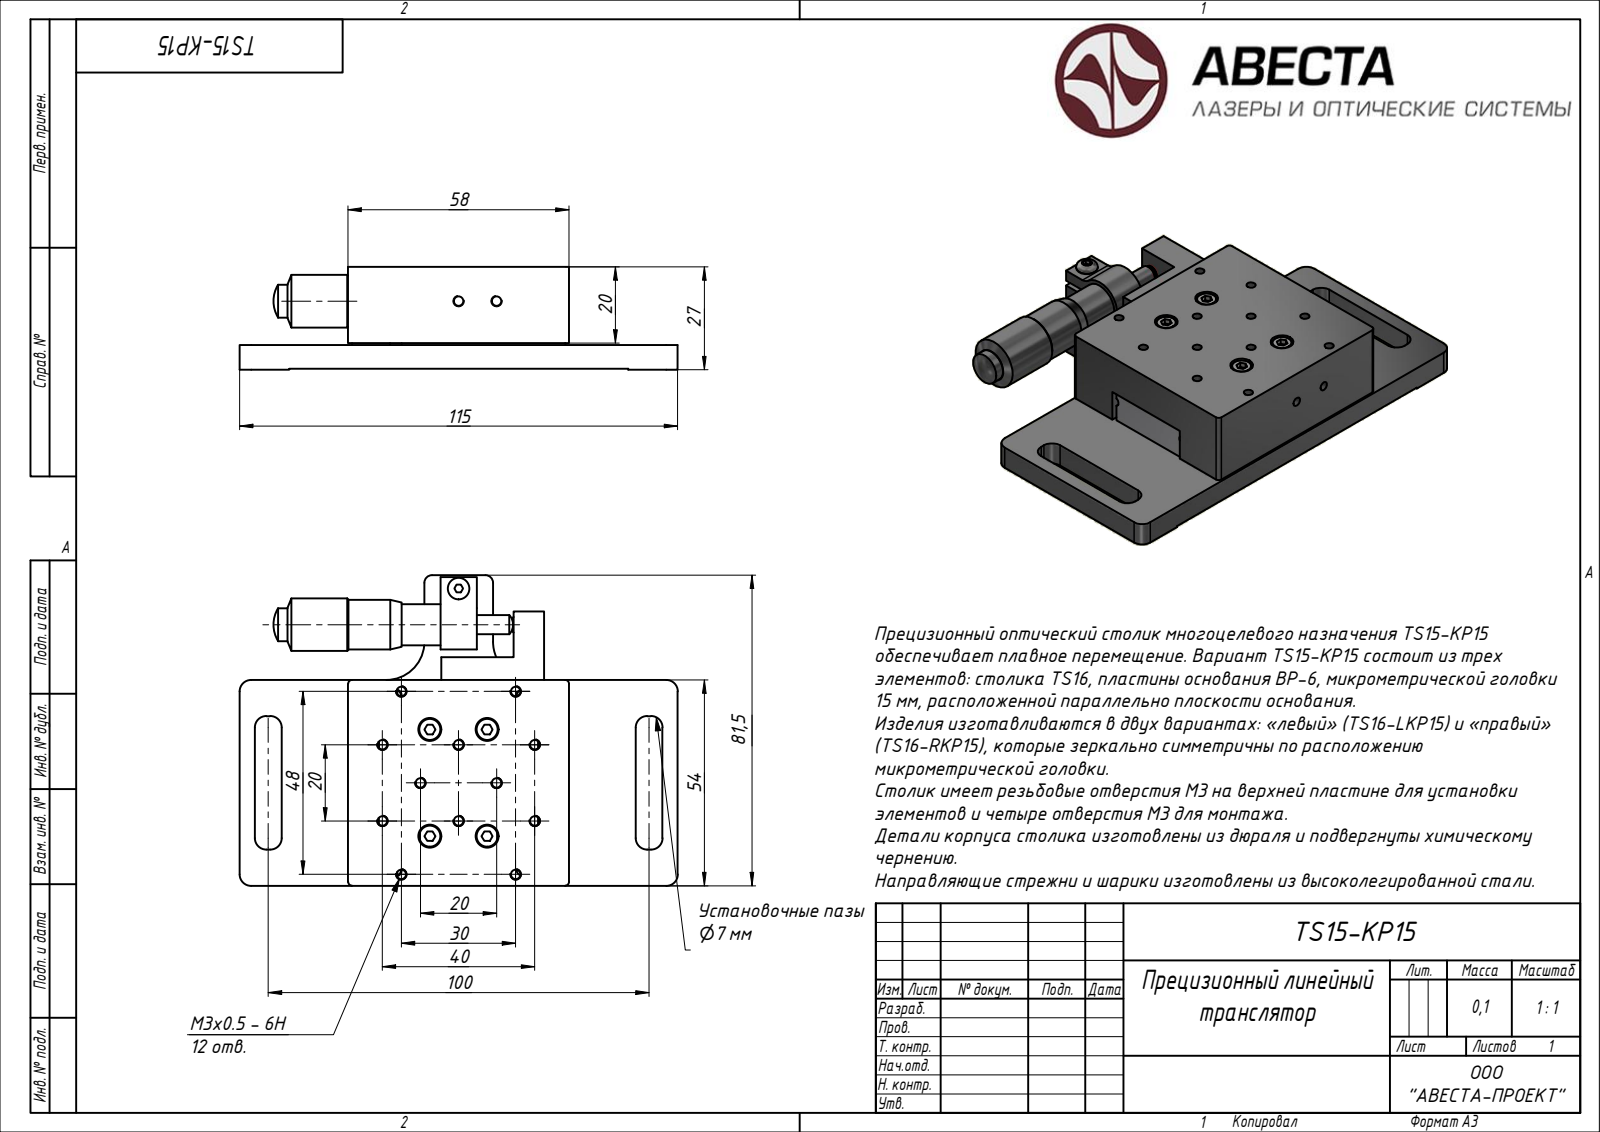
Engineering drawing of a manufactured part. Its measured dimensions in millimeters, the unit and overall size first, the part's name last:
Units: millimetres
Overall size (bounding box): 115 × 81.5 × 27
Bodies: 10 solids, 621 faces (0 planar, 0 cylindrical, 621 other)
Part name (STEP PRODUCT): Block 01
STEP written by: ST-DEVELOPER v15 (AUTOMOTIVE_DESIGN)
